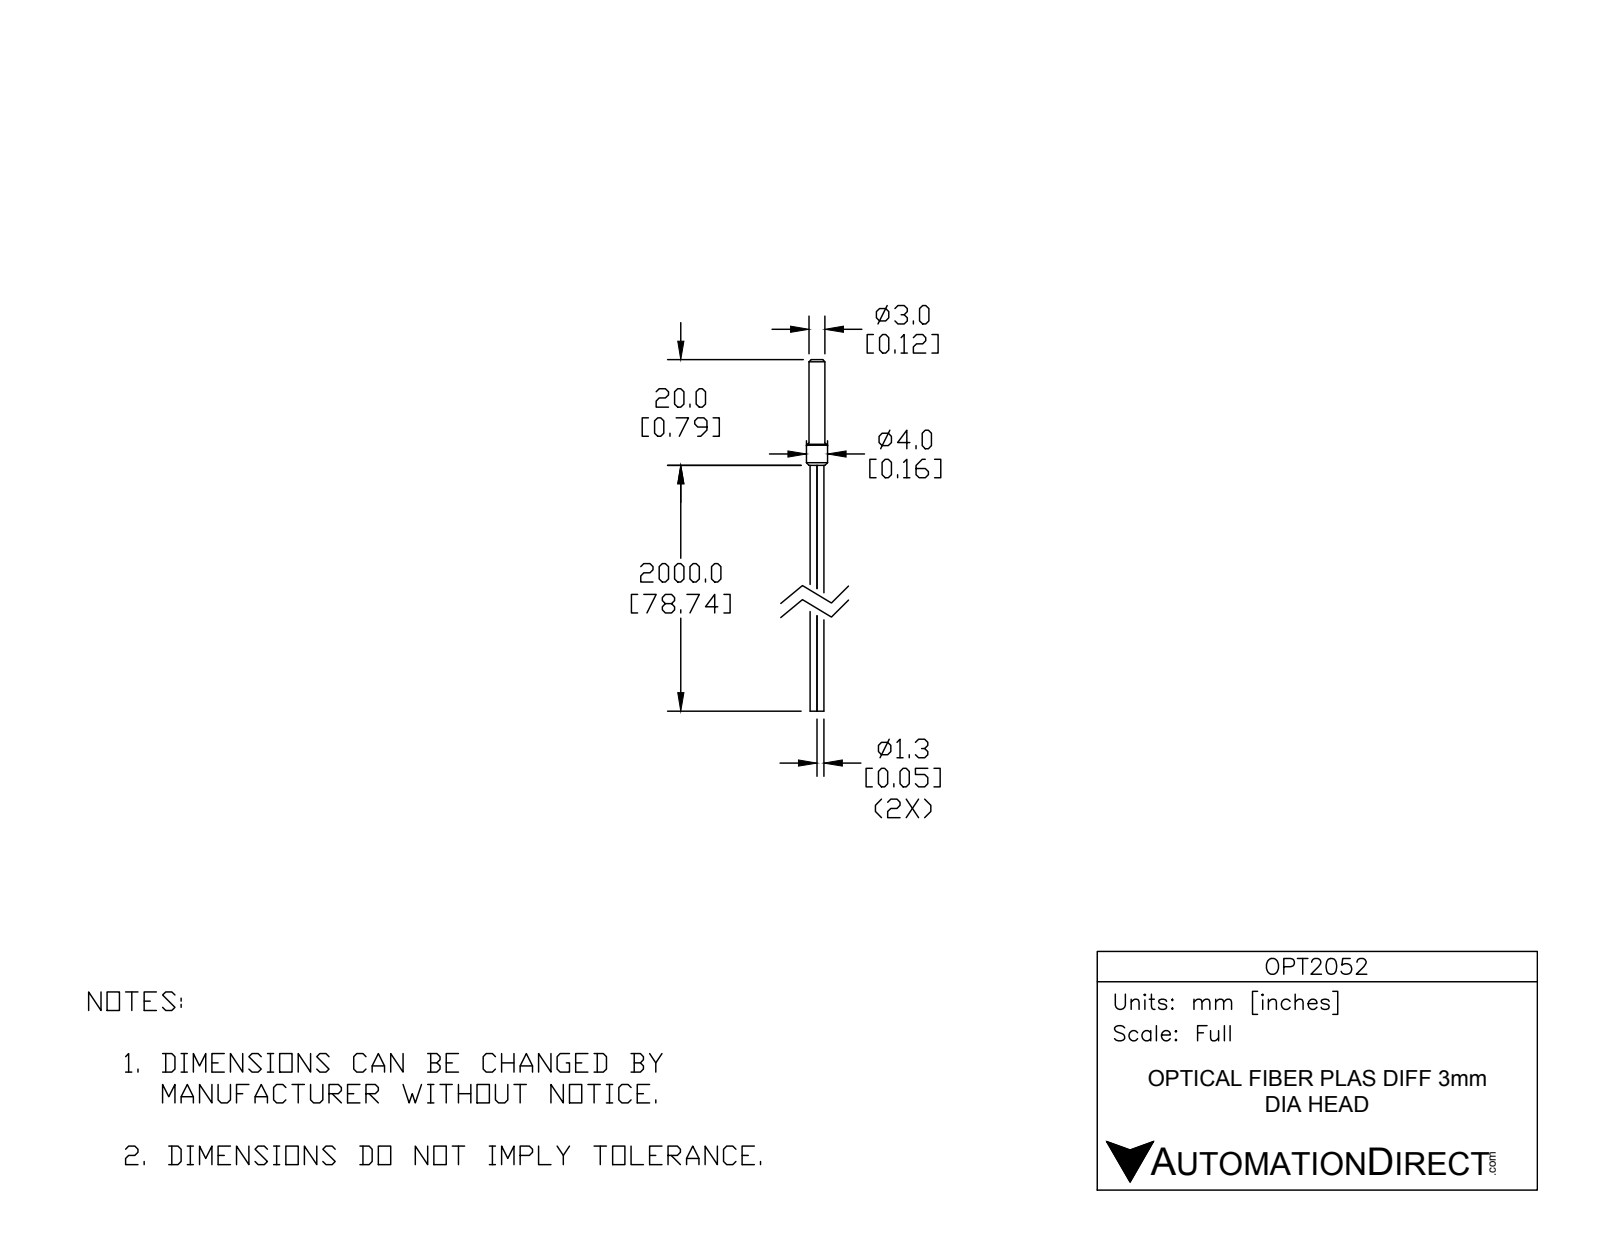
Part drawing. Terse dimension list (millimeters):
name: OPT2052
written by: SolidWorks 2014 (AUTOMOTIVE_DESIGN)
unit: mm
bodies: 1 solid, 19 faces (3 planar, 8 cylindrical, 8 other)
size: 66.5 × 4 × 4
volume: 280 mm³; area: 592 mm²
bosses: 2× ⌀1.3, 1× ⌀4, 1× ⌀3
face distances: 20, 46.5, 66.5
